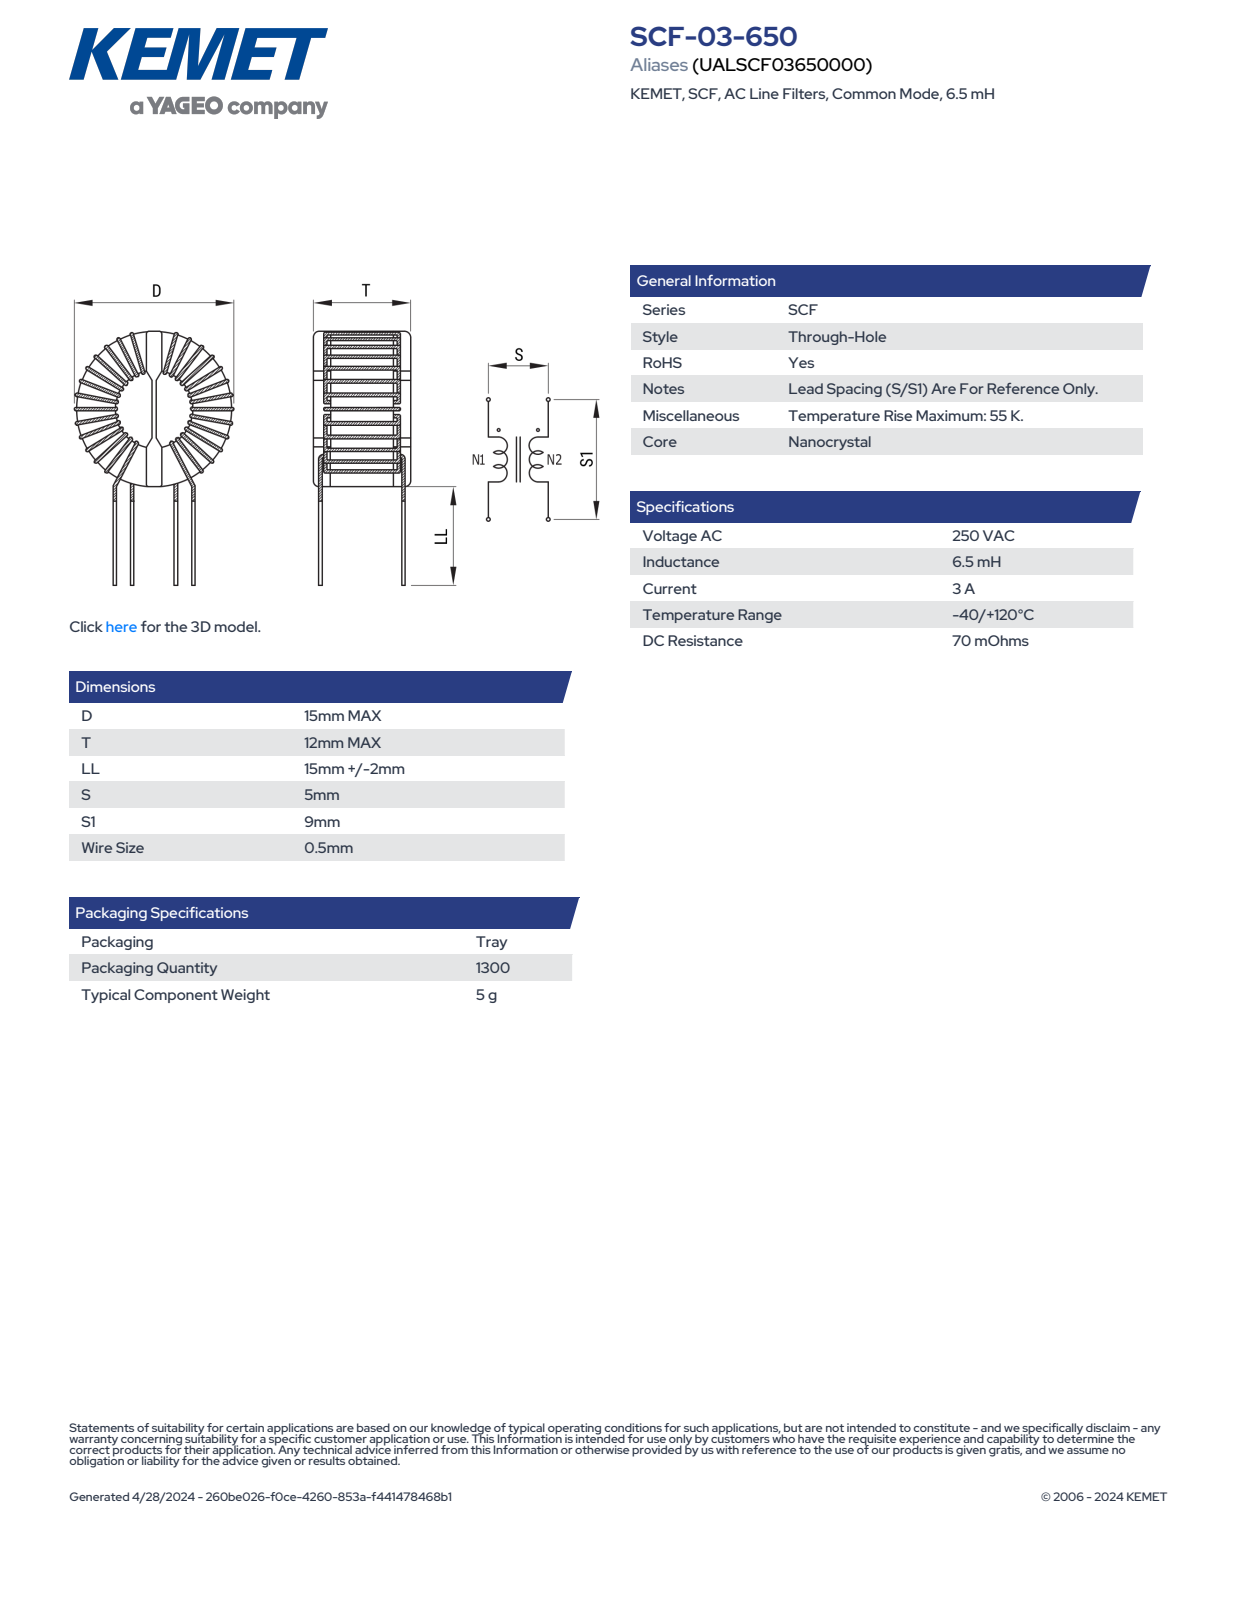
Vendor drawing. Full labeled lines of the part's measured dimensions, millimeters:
Part name (STEP PRODUCT): SCF-03-650
STEP written by: SolidWorks 2018 (AUTOMOTIVE_DESIGN)
Units: millimetres
Bodies: 1 solid, 199 faces (85 planar, 56 cylindrical, 58 other)
Overall size (bounding box): 28.73 × 15 × 12
Volume: 1 668 mm³ · Surface area: 1 262 mm²
Round bosses / shafts (diameter × count): ⌀0.5 ×8
Partial cylindrical surfaces — rounded edges, fillets, slot ends (radius × count): R0.25 ×16, R2 ×1, R3 ×1, R6.4 ×1, R6.4 ×1, R7.5 ×1
Main face-to-face distances: 10.9, 0.55, 11.45, 0.85, 0.88, 1.72, 1.73, 2.6, 0.87, 1.98
